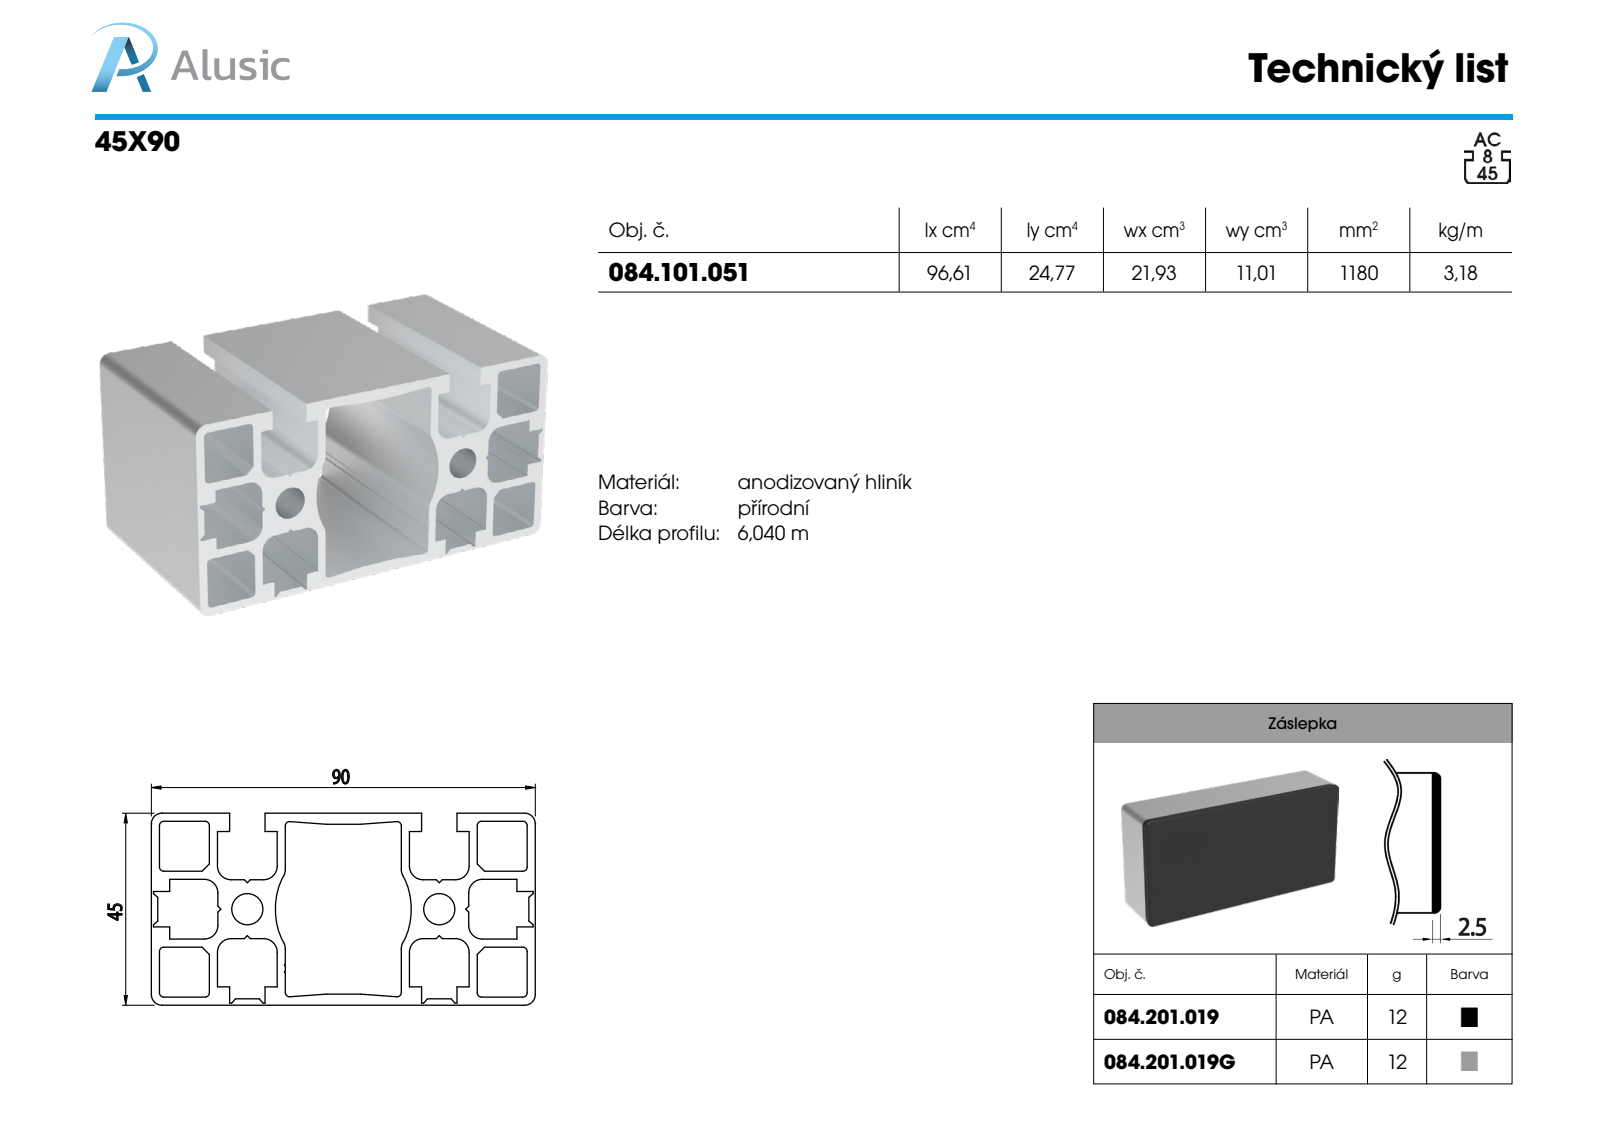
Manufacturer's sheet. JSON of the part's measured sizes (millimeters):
{"part_name": "084.101.051", "step_written_by": "SolidWorks 2018 (AUTOMOTIVE_DESIGN)", "units": "millimeters", "bodies": {"solids": 1, "faces": 167, "planar": 122, "cylindrical": 45, "other": 0}, "overall_size": [100, 90, 45], "volume_mm3": 117575, "surface_area_mm2": 95860, "round_holes": [[7.3, 2]], "partial_cylinders_radius": [[1, 16], [3.2, 12], [2.5, 4], [3, 4], [16.64, 2], [0.2, 1]], "face_to_face_distances": [1.9, 45, 29.5, 13.6, 15.9, 31.4, 58.6, 11.7, 43.1, 74.5], "hole_center_spacings": [45]}
